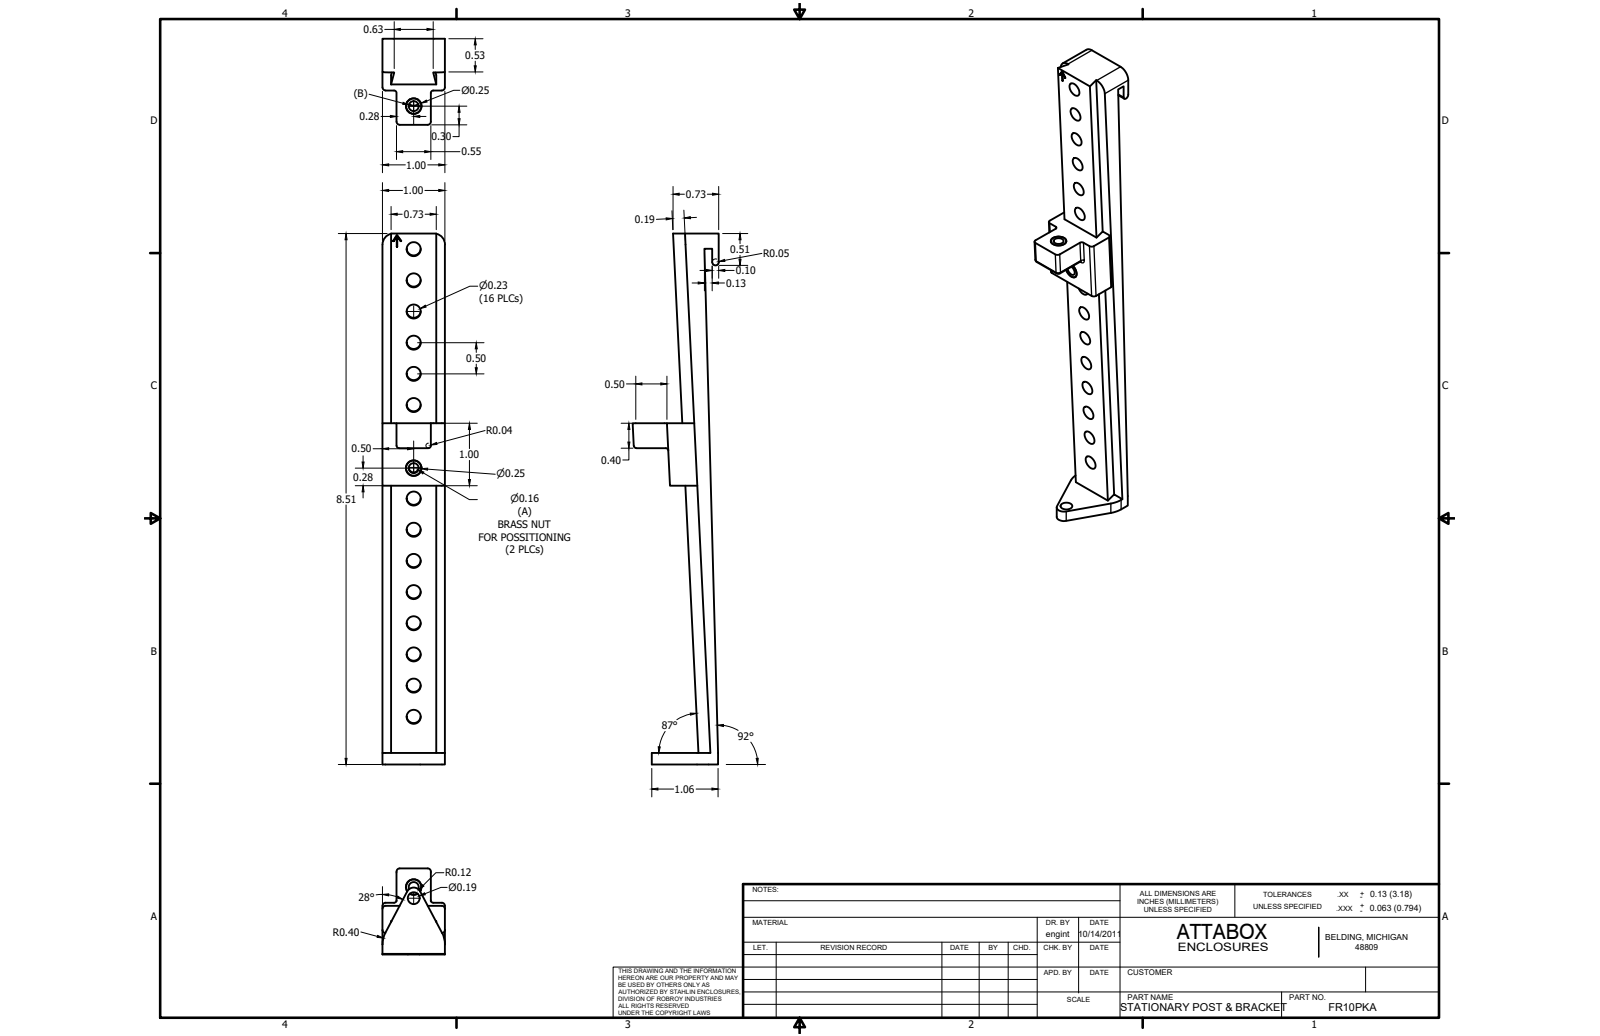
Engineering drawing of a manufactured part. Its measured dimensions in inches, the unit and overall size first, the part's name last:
Units: inches
Overall size (bounding box): 20.754 × 16.753 × 8.703
Round holes (diameter × count): ⌀0.25 ×64, ⌀0.217 ×4, ⌀0.22 ×4
Round bosses / shafts (diameter × count): ⌀0.433 ×4, ⌀0.373 ×4, ⌀0.19 ×4
Partial cylindrical surfaces — rounded edges, fillets, slot ends (radius × count): R0.01 ×156, R0.06 ×12, R0.049 ×4, R0.23 ×4
Main face-to-face distances: 24.021, 1, 10.096, 13.925, 11.096, 12.925, 2.828, 0.203, 10.299, 11.299
Hole centre spacings: 0.5, 2.873, 1, 3, 1.5, 3.202, 2, 3.465
Volume: 11.8 in³ · Surface area: 134.8 in²
Bodies: 12 solids, 2068 faces (1156 planar, 272 cylindrical, 640 other)
Part name (STEP PRODUCT): FR10POST
STEP written by: SolidWorks 2019 (AUTOMOTIVE_DESIGN)
